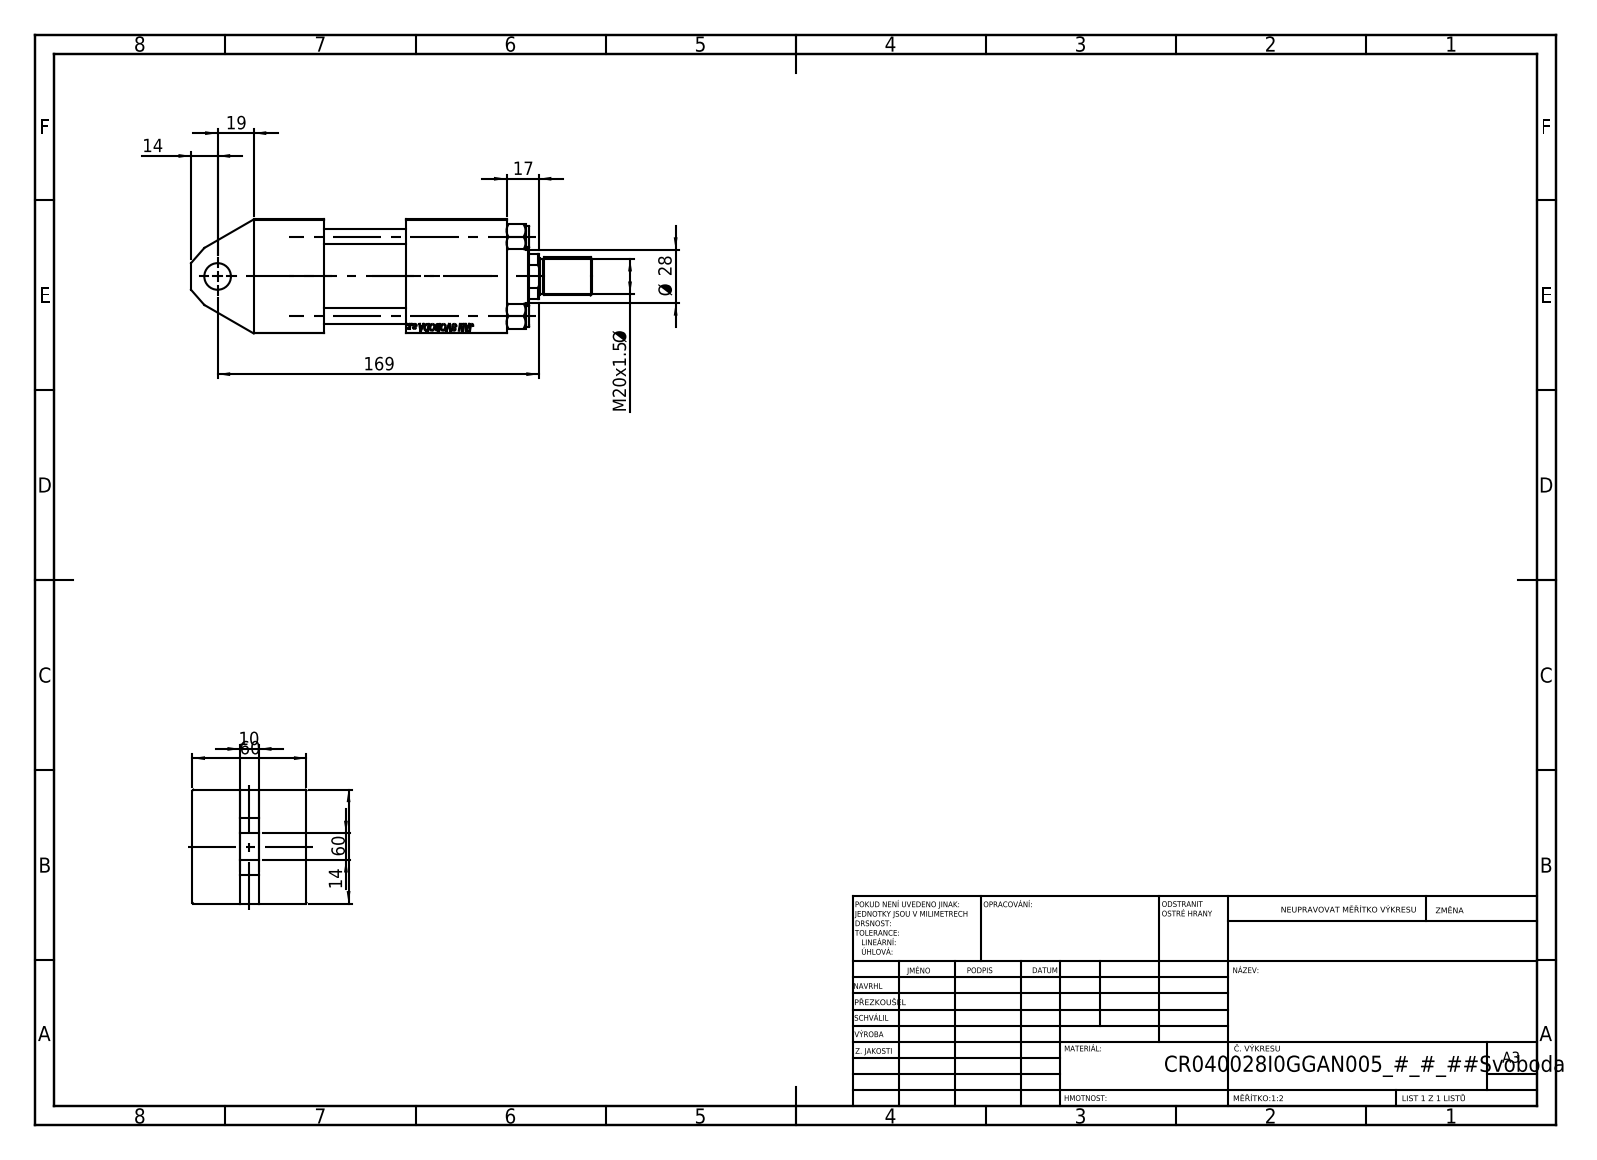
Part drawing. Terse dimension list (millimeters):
name: V215_VC_A; V215CR_I_Body; ROD_END_AH; V215CR_TYCINKA_I (+2 more)
written by: SolidWorks 2019 (CONFIG_CONTROL_DESIGN)
unit: mm
bodies: 12 solids, 1092 faces (506 planar, 84 cylindrical, 502 other)
size: 211 × 60 × 60
volume: 418 280 mm³; area: 110 118 mm²
holes: 4× ⌀8, 2× ⌀7, 2× ⌀16.66, 2× ⌀24, 1× ⌀14, 1× ⌀18.5, 1× ⌀28, 1× ⌀31, 1× ⌀40, 1× ⌀45
bosses: 4× ⌀11, 1× ⌀46, 1× ⌀42, 1× ⌀20, 1× ⌀18
rounds: 1× R13.5
face distances: 60, 37, 35, 25, 80, 43, 53, 133, 96, 104.3
hole spacings: 29.49, 41.7, 58.97, 77.5
